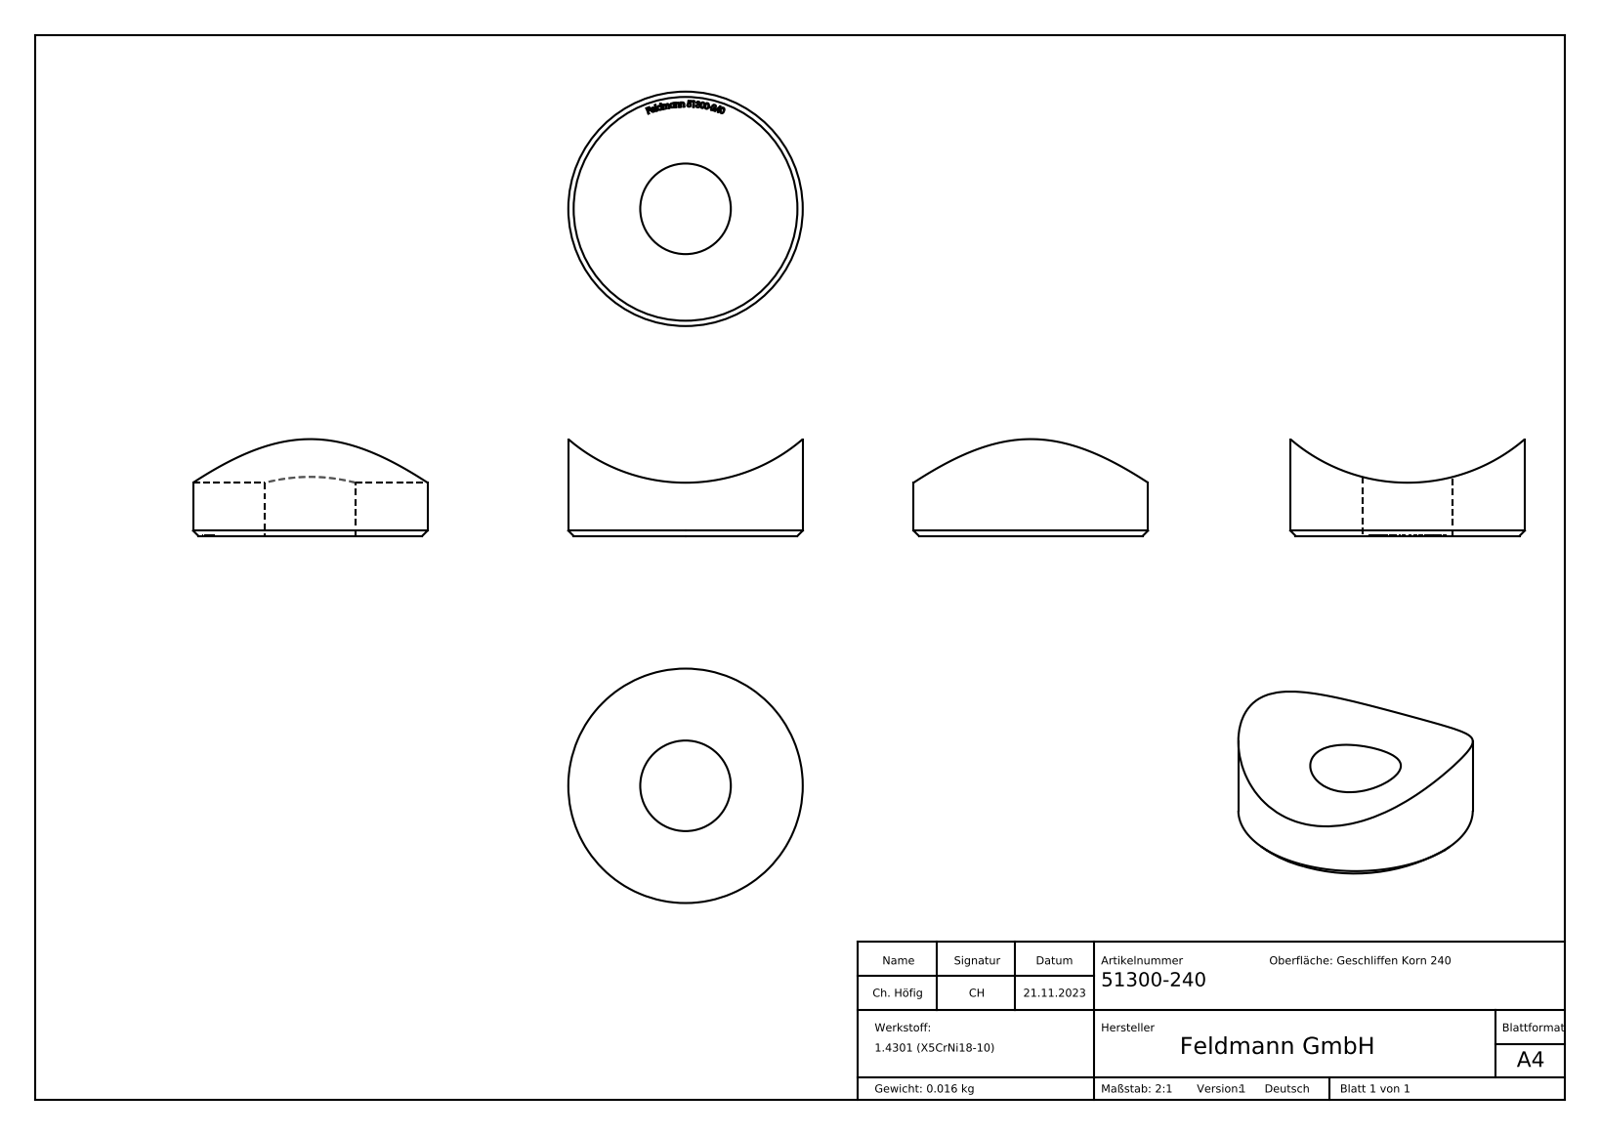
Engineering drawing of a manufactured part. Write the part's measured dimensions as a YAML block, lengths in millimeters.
part_name: "51300-240"
step_written_by: "SolidWorks 2018 (CONFIG_CONTROL_DESIGN)"
units: millimeters
bodies: {solids: 1, faces: 224, planar: 117, cylindrical: 3, other: 104}
overall_size: [22, 22, 9.09]
volume: 1964
surface_area: 1277
round_holes:
  - {diameter: 8.5, count: 1}
round_bosses_or_shafts:
  - {diameter: 22, count: 1}
partial_cylinders:
  - {radius: 16.85, count: 1}
face_to_face_distances: [0.34, 0.32, 0.54, 0.53, 0.48, 0.59, 0.39, 0.52, 0.47, 0.31]
